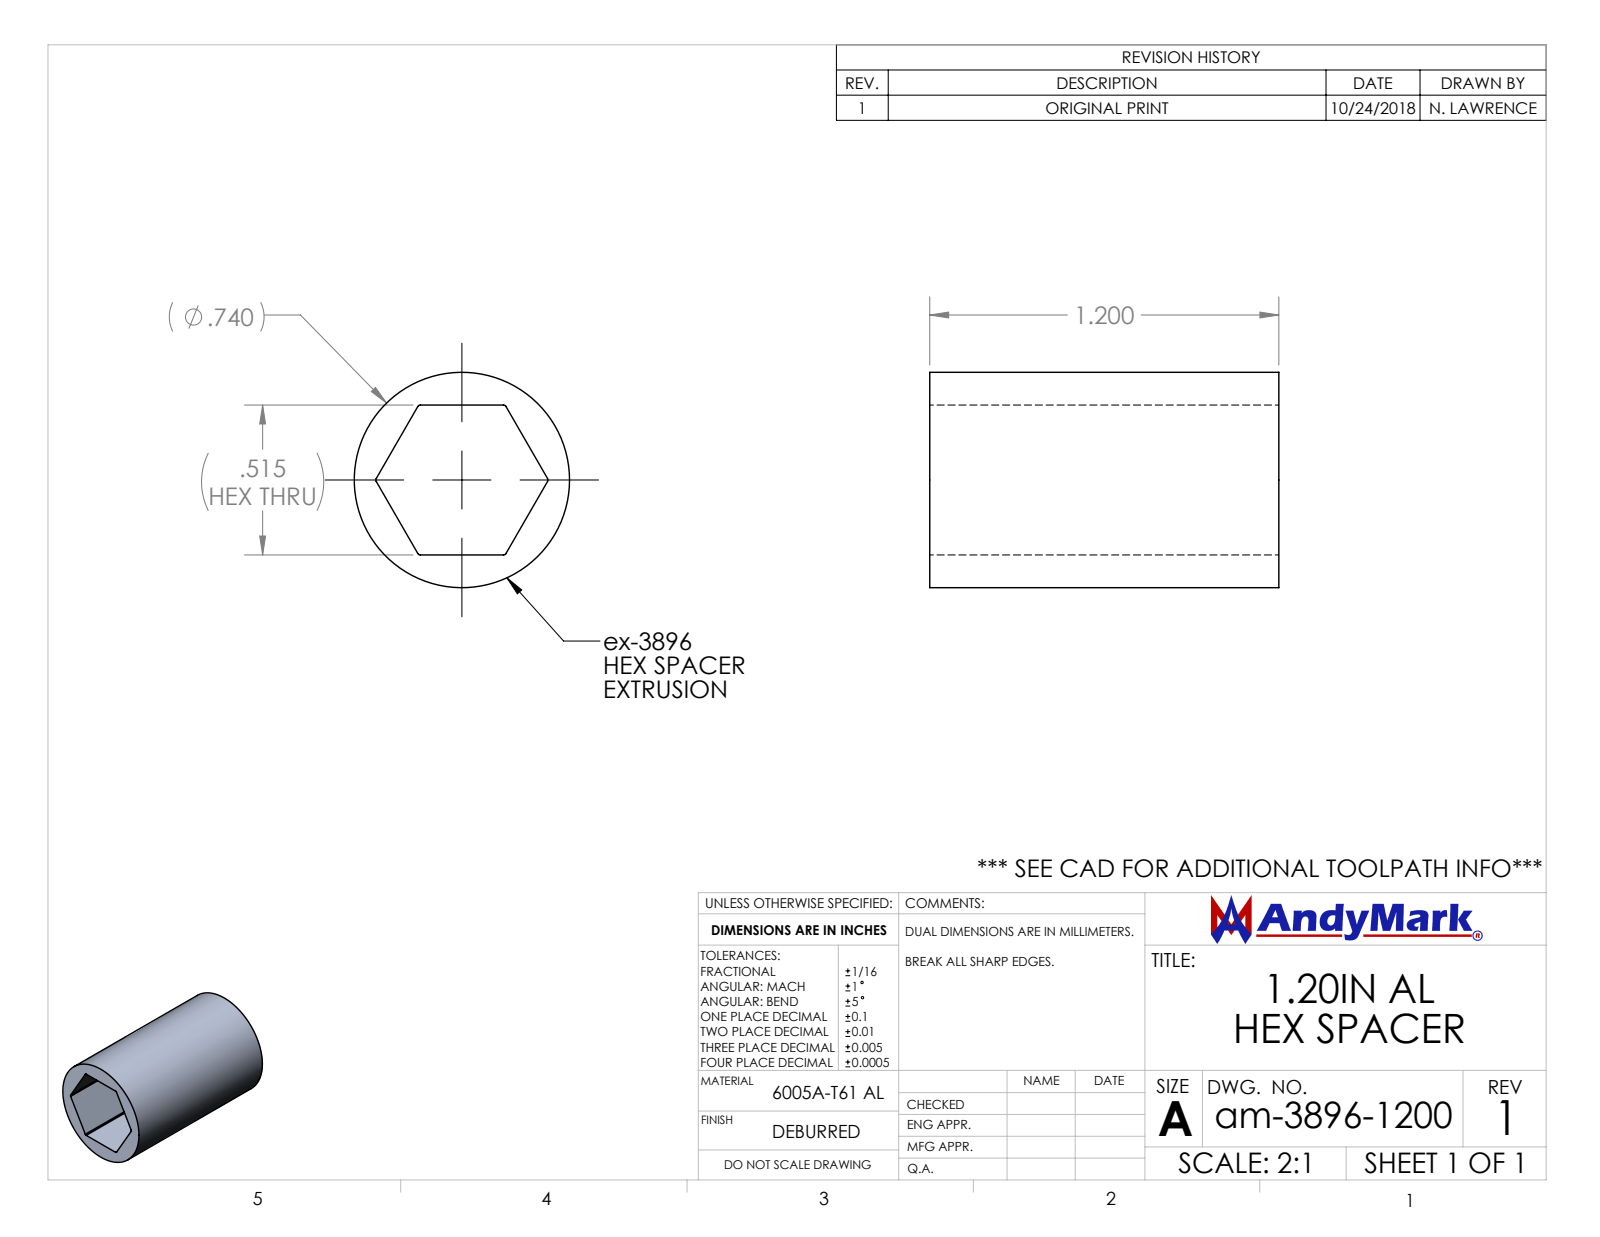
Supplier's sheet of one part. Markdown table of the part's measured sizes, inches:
| quantity | value |
| --- | --- |
| part name | am-3896-1200 1.20in Hex Spacer Extrusion |
| STEP written by | SolidWorks 2021 (CONFIG_CONTROL_DESIGN) |
| units | inches |
| bodies | 1 solid, 17 faces (8 planar, 9 cylindrical, 0 other) |
| overall size | 1.2 × 0.74 × 0.74 |
| volume | 0.241 in³ |
| surface area | 5.324 in² |
| round bosses / shafts (diameter × count) | 0.74 × 1 |
| partial cylindrical surfaces (radius × count) | 0.01 × 6 |
| main face-to-face distances | 0.515, 1.2 |
